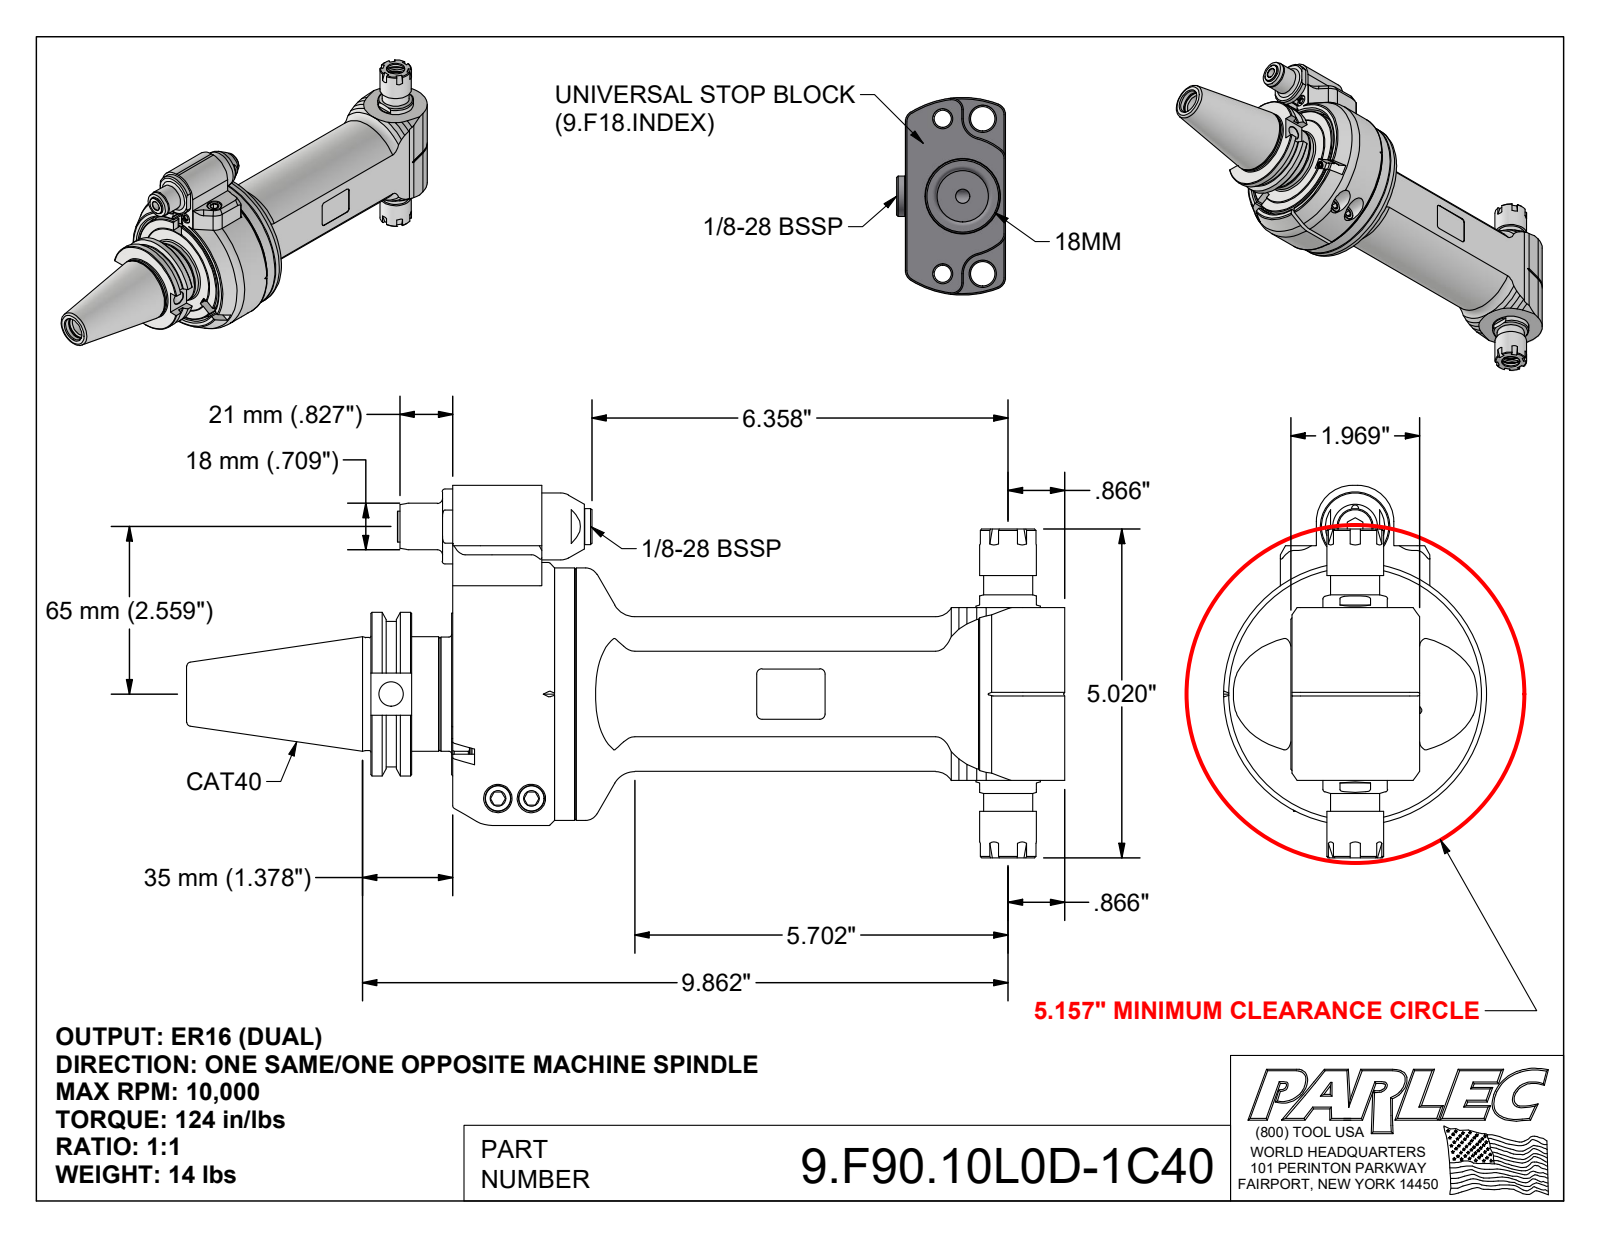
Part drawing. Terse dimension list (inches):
name: 9.F90.10L0D-1C40; 9_F90_10L00_2U; 9_GA
written by: Autodesk Inventor 2025 (AUTOMOTIVE_DESIGN)
unit: in
bodies: 4 solids, 664 faces (307 planar, 164 cylindrical, 193 other)
size: 13.415 × 5.689 × 4.016
volume: 66.8 in³; area: 234.9 in²
holes: 4× ⌀0.126, 3× ⌀0.197, 3× ⌀0.256, 3× ⌀0.433, 2× ⌀0.102, 2× ⌀0.13, 2× ⌀0.165, 2× ⌀0.315, 2× ⌀0.409, 2× ⌀0.492, 1× ⌀0.098, 1× ⌀0.118
bosses: 4× ⌀0.394, 2× ⌀0.866, 2× ⌀0.709, 2× ⌀0.472, 2× ⌀0.315, 2× ⌀0.236, 2× ⌀0.098, 1× ⌀4.016
rounds: 14× R0.039, 12× R0.079, 6× R0.118, 4× R0.157, 2× R0.016, 2× R0.02, 2× R0.315, 2× R0.551
face distances: 0.02, 1.969, 0.039, 0.276, 0.295, 1.26, 0.335, 1.555, 1.28, 1.299
hole spacings: 0.325, 0.459, 0.276, 0.504, 0.65, 0.74, 0.996, 1.596
